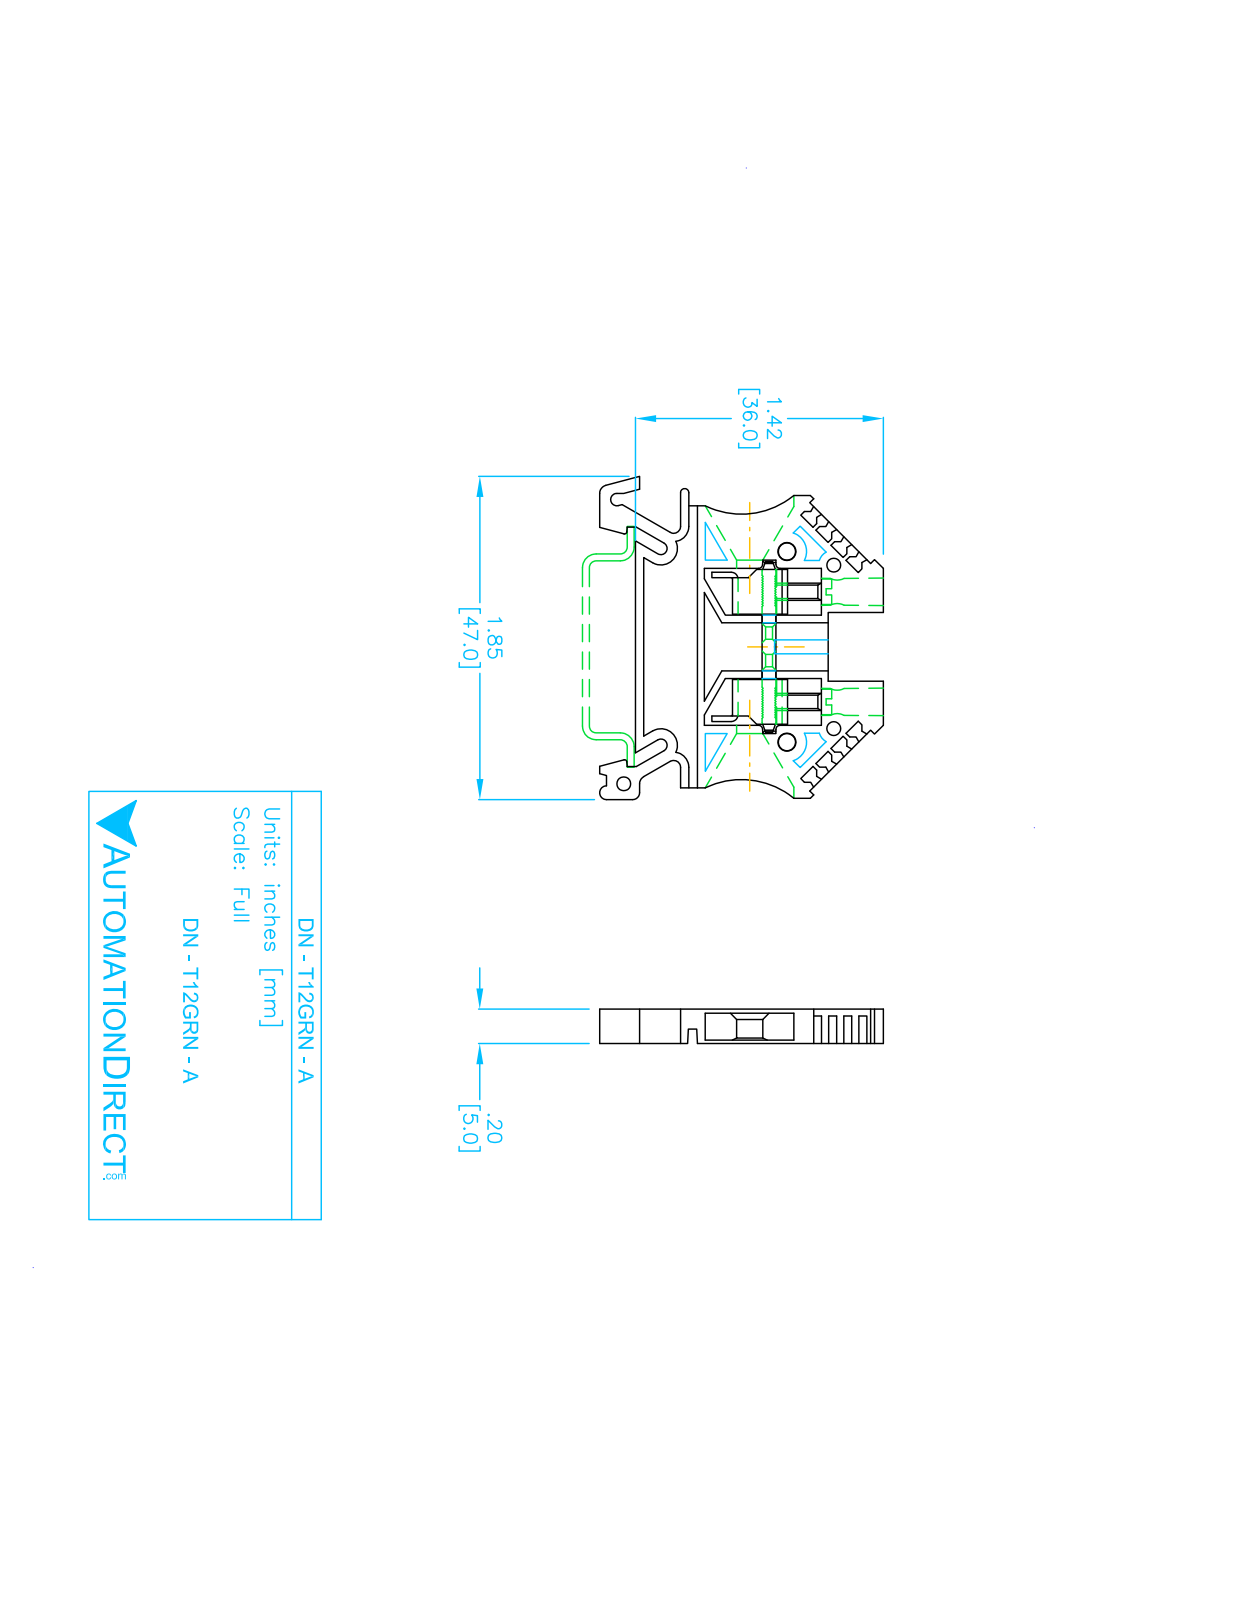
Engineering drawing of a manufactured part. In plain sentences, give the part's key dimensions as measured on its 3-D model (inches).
The part is named "DN-T12GRN-A". Its 3-D file was written by "SolidWorks 2017 (AUTOMOTIVE_DESIGN)". It is 1 solid with 169 faces: 134 planar, 35 cylindrical and 0 other. Overall it measures 1.85 by 1.622 by 0.197 inches. Its volume is 0.306 cubic inches and its surface area 7.131 square inches. Round holes: 2 of diameter 0.164, 1 of diameter 0.079. Partial cylindrical surfaces (rounded edges, fillets, slot ends): 4 of radius 0.039, 3 of radius 0.035, 2 of radius 0.012, 2 of radius 0.047, 2 of radius 0.087, 2 of radius 0.094, 2 of radius 0.472, 1 of radius 0.024. The main face-to-face distances are 0.189, 0.197, 0.087, 0.02, 0.106, 0.094, 0.114, 0.083, 0.102, 0.354. The hole center spacings are 0.589.
